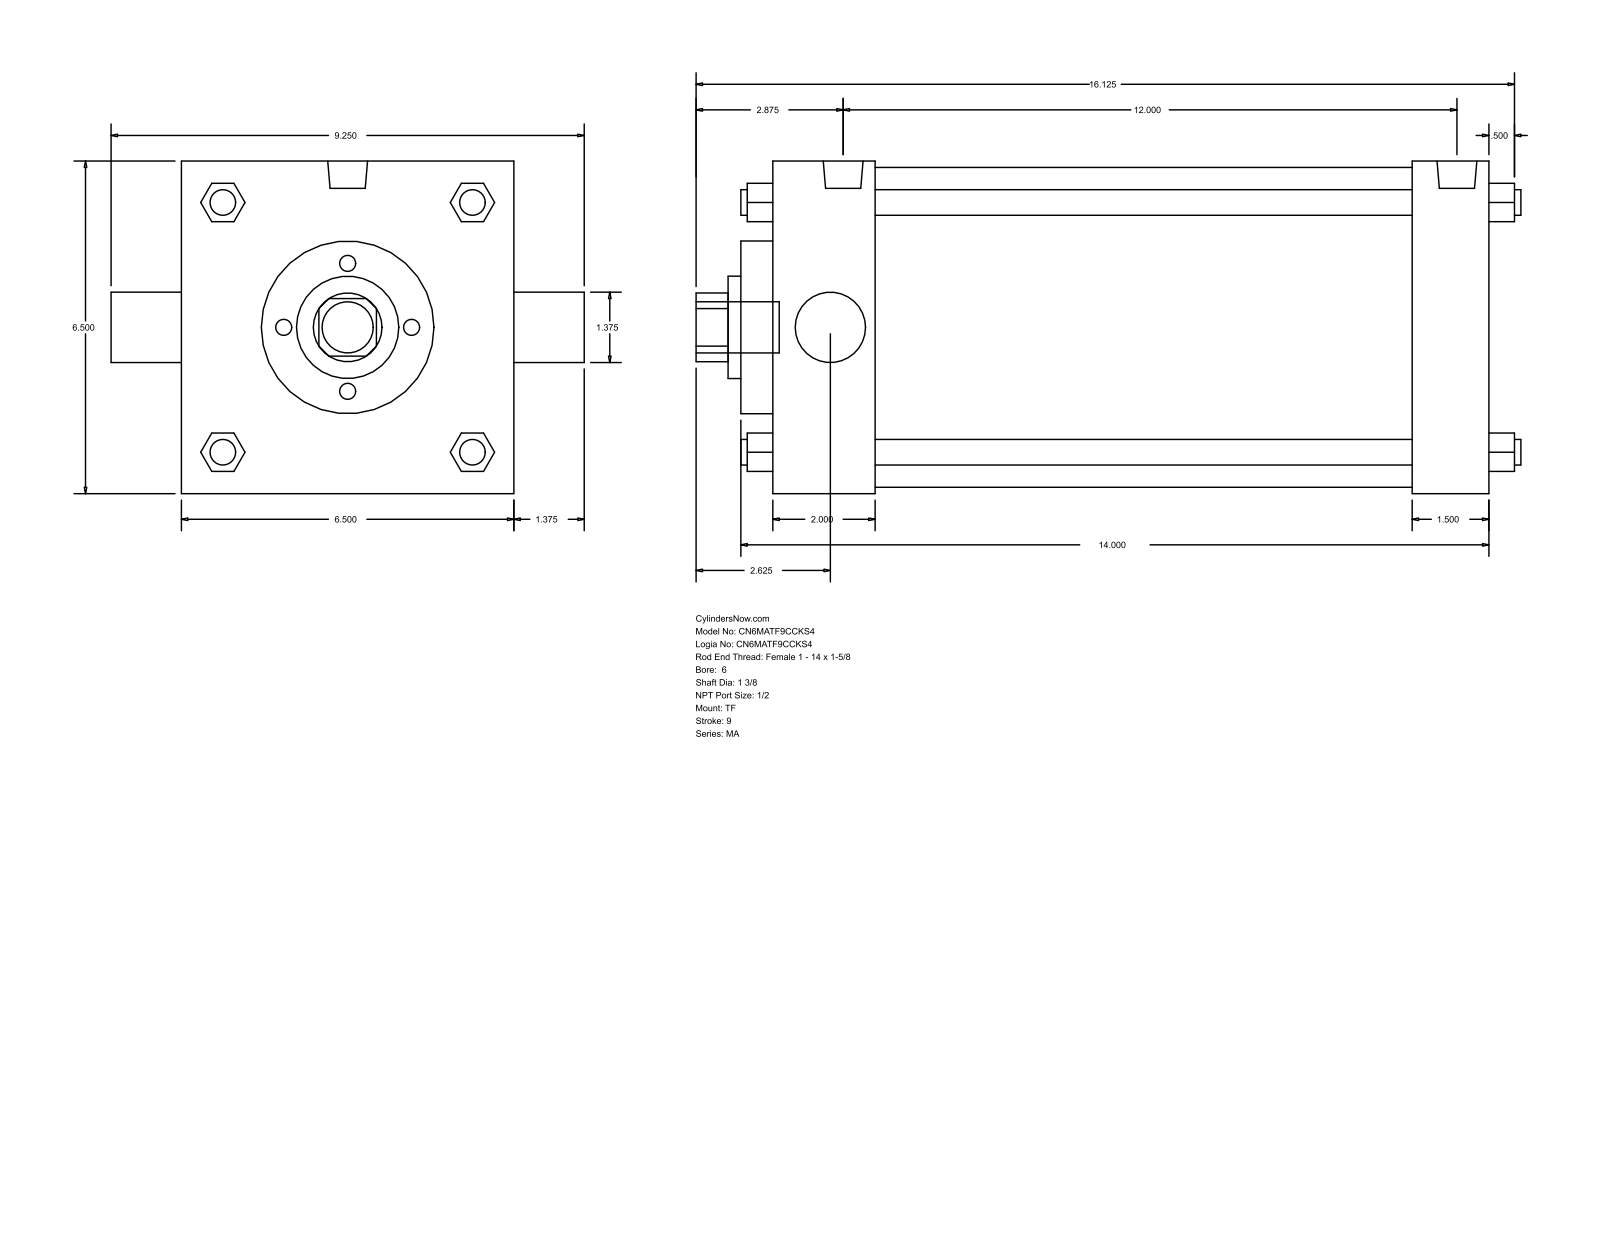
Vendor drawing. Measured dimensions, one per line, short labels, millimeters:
name: MA_TF__0600_1.375
written by: GSSL Pune (CONFIG_CONTROL_DESIGN)
unit: mm
bodies: 0 solids, 122 faces (93 planar, 29 cylindrical, 0 other)
size: 409.57 × 234.95 × 165.1
holes: 2× ⌀34.92, 1× ⌀50.8, 1× ⌀85.72, 1× ⌀158.75
bosses: 4× ⌀12.7, 3× ⌀17.46, 2× ⌀19.77, 1× ⌀25.4
rounds: 1× R17.06
face distances: 165.1, 358.78, 50.8, 320.67, 307.98, 269.87, 38.11, 15.87, 66.67, 336.54
